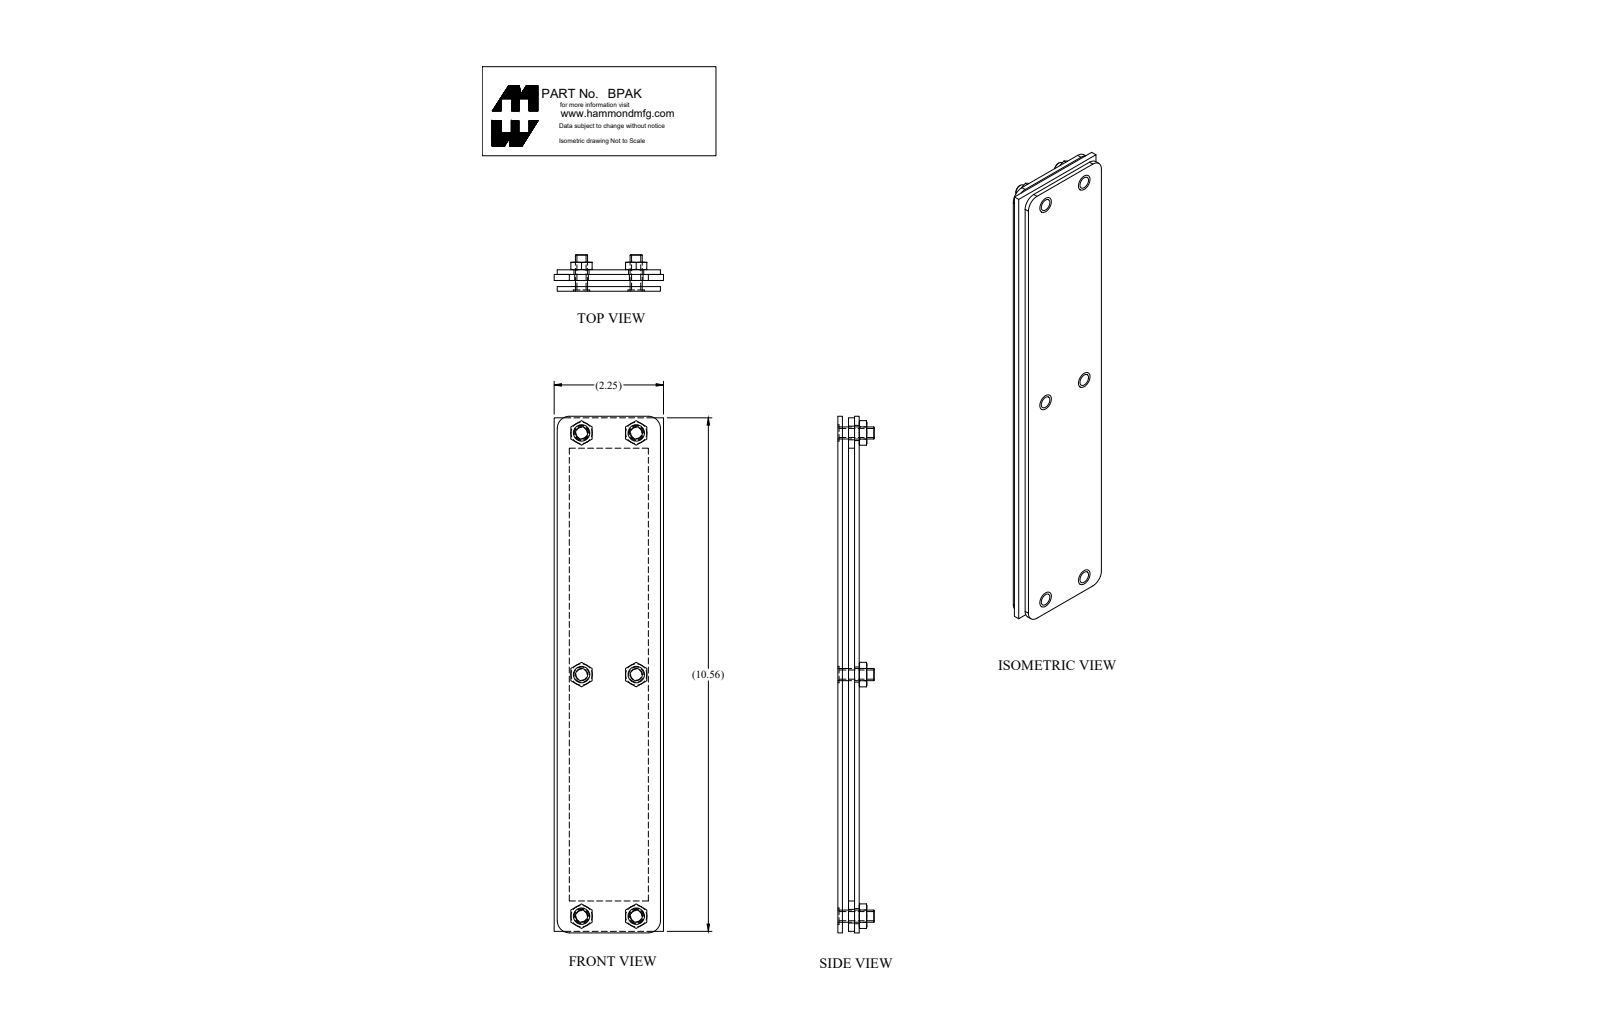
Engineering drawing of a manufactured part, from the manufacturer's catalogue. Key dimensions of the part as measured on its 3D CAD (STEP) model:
Part name (STEP PRODUCT): BPAK_Default
STEP written by: SolidWorks 2019 (CONFIG_CONTROL_DESIGN)
Units: inches
Bodies: 15 solids, 254 faces (88 planar, 76 cylindrical, 90 other)
Overall size (bounding box): 10.625 × 2.25 × 0.75
Volume: 5.59 in³ · Surface area: 125.6 in²
Round holes (diameter × count): ⌀0.25 ×6, ⌀0.313 ×6, ⌀0.281 ×4
Round bosses / shafts (diameter × count): ⌀0.337 ×6
Partial cylindrical surfaces — rounded edges, fillets, slot ends (radius × count): R0.25 ×4
Main face-to-face distances: 0.345, 0.095, 0.44, 0.25, 0.125, 0.125, 0.22, 0.22, 0.063, 2.187
Hole centre spacings: 1.125, 4.969, 4.969, 4.969, 5.094, 5.094, 5.095, 9.938
